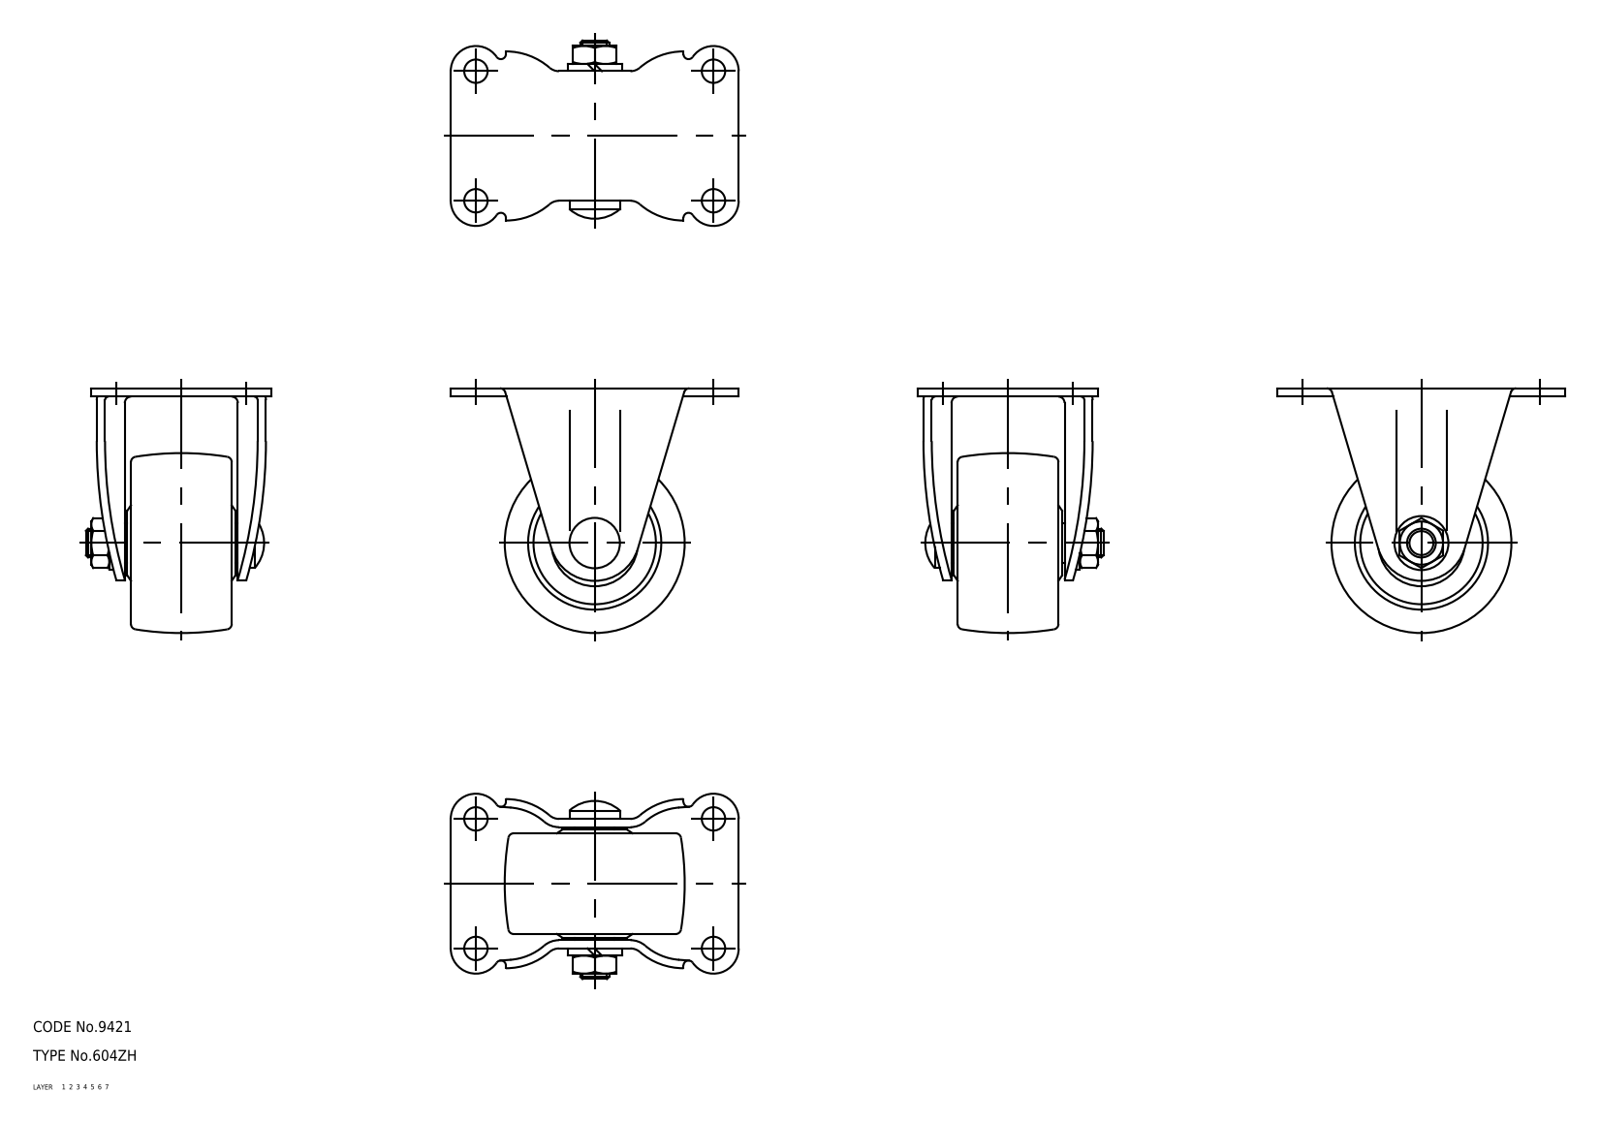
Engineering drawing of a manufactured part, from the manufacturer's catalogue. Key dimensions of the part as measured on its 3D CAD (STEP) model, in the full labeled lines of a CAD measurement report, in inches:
Part name (STEP PRODUCT): wheel; axle; No_604ZH_14956_36
STEP written by: CADfix (AUTOMOTIVE_DESIGN)
Units: inches
Bodies: 3 solids, 148 faces (0 planar, 0 cylindrical, 148 other)
Overall size (bounding box): 3.15 × 2.677 × 2.028
Volume: 4.251 in³ · Surface area: 38.8 in²
